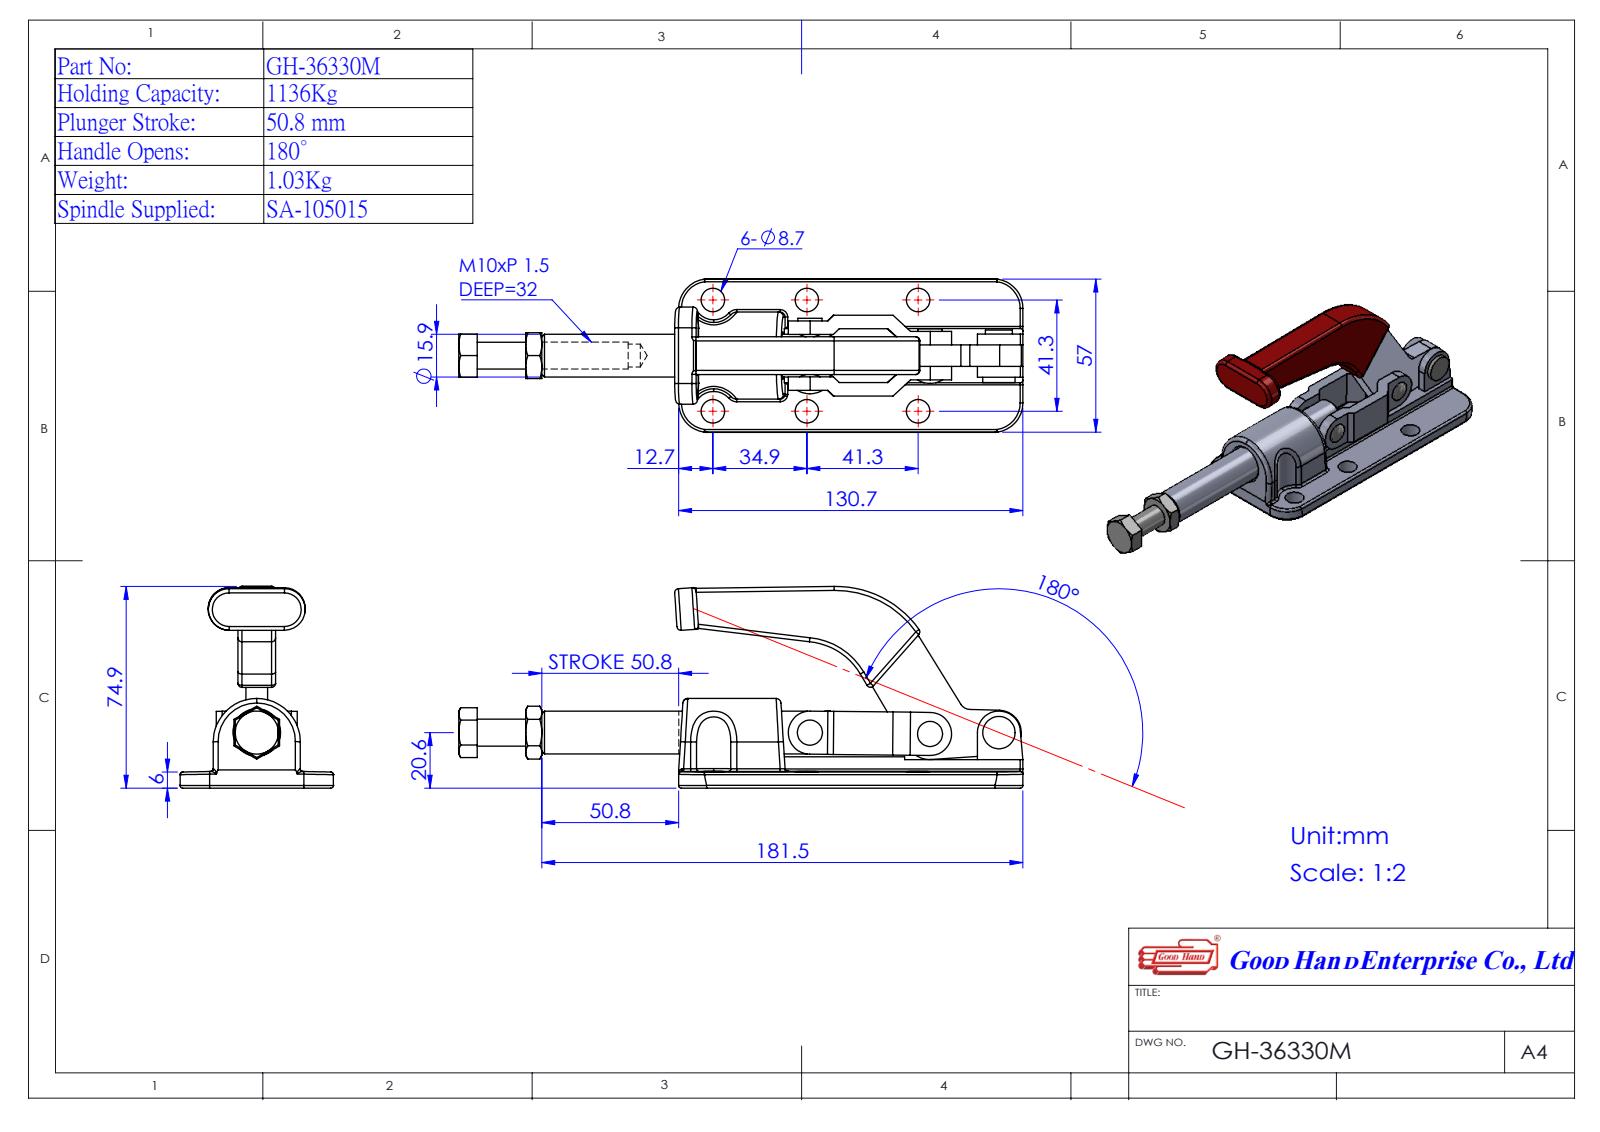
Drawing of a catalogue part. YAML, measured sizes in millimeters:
part_name: "136330M01-1^EMC36330; Group3^EMC36330; Group2^EMC36330; Group4^EMC36330 (+2 more)"
step_written_by: "SolidWorks 2016 (AUTOMOTIVE_DESIGN)"
units: millimeters
bodies: {solids: 4, faces: 188, planar: 97, cylindrical: 61, other: 30}
overall_size: [209.44, 74.87, 57]
volume: 123164
surface_area: 49730
round_holes:
  - {diameter: 8.7, count: 6}
  - {diameter: 6, count: 3}
  - {diameter: 15, count: 1}
round_bosses_or_shafts:
  - {diameter: 10, count: 2}
  - {diameter: 9, count: 2}
  - {diameter: 15.9, count: 1}
  - {diameter: 12, count: 1}
  - {diameter: 11, count: 1}
partial_cylinders:
  - {radius: 11, count: 4}
  - {radius: 8, count: 3}
  - {radius: 0.8, count: 2}
  - {radius: 8.5, count: 2}
  - {radius: 4, count: 1}
  - {radius: 8.3, count: 1}
  - {radius: 9.5, count: 1}
  - {radius: 16.16, count: 1}
face_to_face_distances: [3, 11, 8, 14, 1, 5, 6, 17, 16, 19]
hole_center_spacings: [41.3, 34.9, 54.07, 58.41, 76.2, 86.67, 25.59, 44.6]
